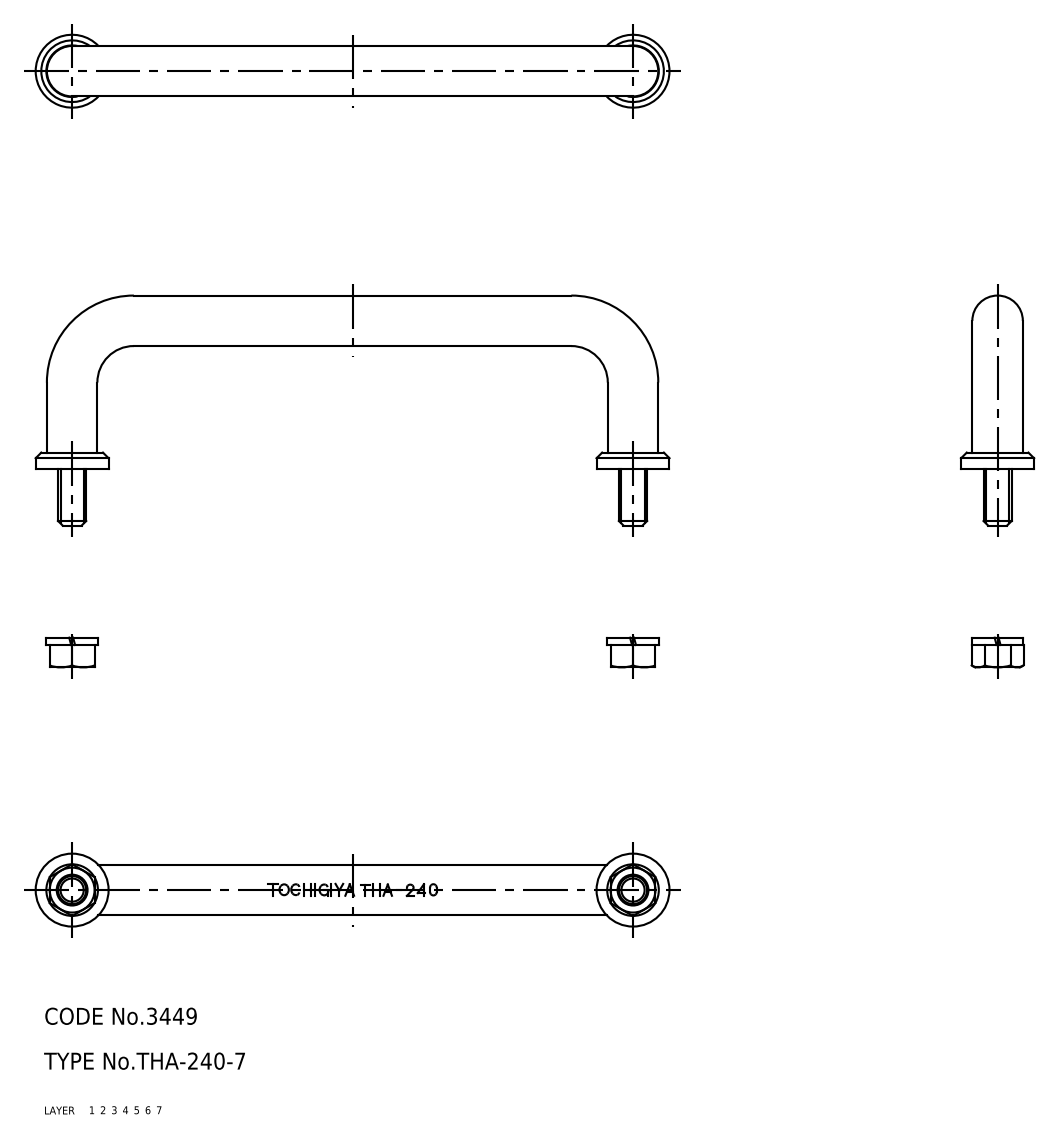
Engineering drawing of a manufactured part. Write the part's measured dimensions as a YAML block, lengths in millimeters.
part_name: "pull; THA_240_7; washer; facing ring (+1 more)"
step_written_by: "SolidWorks 2015 (AUTOMOTIVE_DESIGN)"
units: millimeters
bodies: {solids: 7, faces: 90, planar: 30, cylindrical: 34, other: 26}
overall_size: [113, 41, 13]
volume: 10280
surface_area: 6028
round_holes:
  - {diameter: 5, count: 2}
  - {diameter: 5.5, count: 2}
  - {diameter: 9.2, count: 2}
round_bosses_or_shafts:
  - {diameter: 9, count: 3}
  - {diameter: 13, count: 2}
face_to_face_distances: [1, 3.3, 4.3, 2, 3, 8, 1.3, 50, 4, 5.3]
hole_center_spacings: [100]
